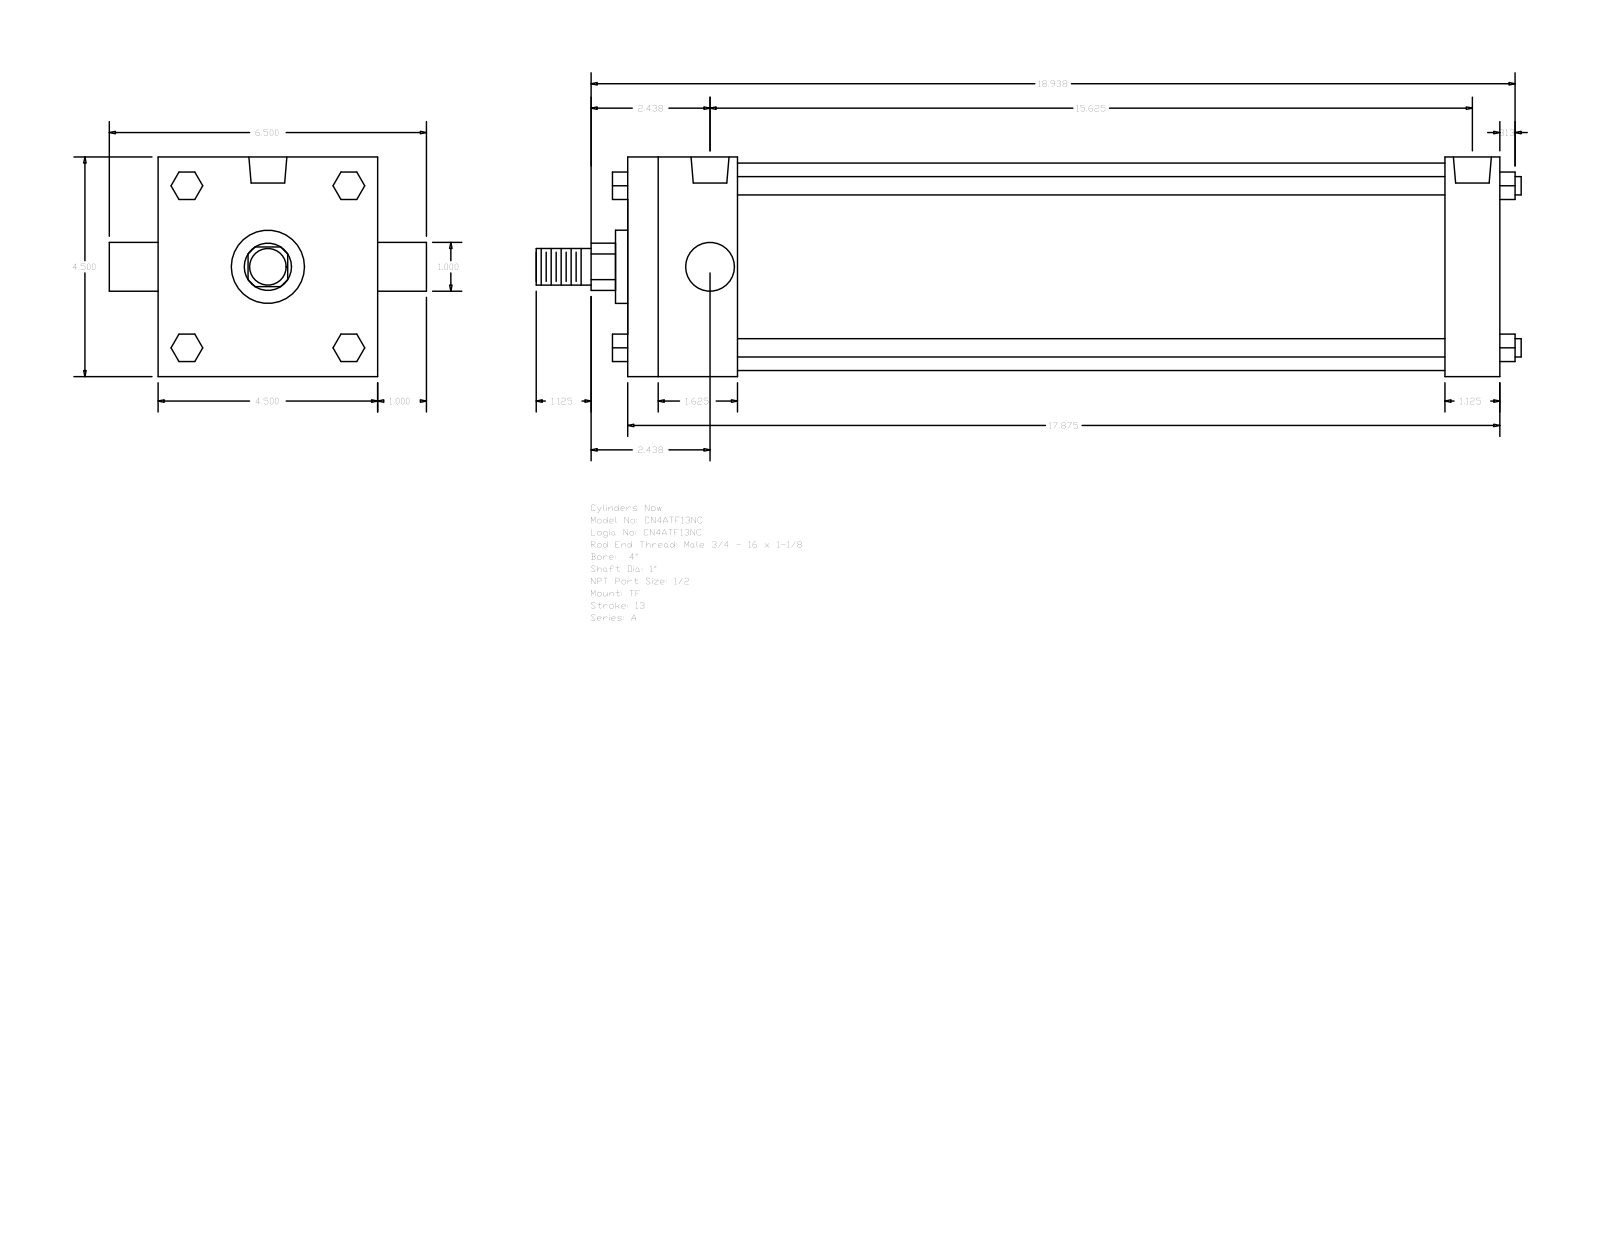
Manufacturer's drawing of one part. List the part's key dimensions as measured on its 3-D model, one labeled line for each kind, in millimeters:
Part name (STEP PRODUCT): A_TF__0400_1
STEP written by: GSSL Pune (CONFIG_CONTROL_DESIGN)
Units: millimetres
Bodies: 0 solids, 120 faces (92 planar, 28 cylindrical, 0 other)
Overall size (bounding box): 512.76 × 165.1 × 114.3
Round holes (diameter × count): ⌀8.73 ×3, ⌀19.77 ×2
Round bosses / shafts (diameter × count): ⌀9.53 ×4, ⌀25.4 ×2, ⌀107.95 ×1, ⌀38.1 ×1, ⌀19.05 ×1
Partial cylindrical surfaces — rounded edges, fillets, slot ends (radius × count): R12.29 ×1
Main face-to-face distances: 114.3, 454.02, 28.57, 425.45, 57.15, 368.3, 396.87, 14.29, 42.16, 73.03
Hole centre spacings: 3.18, 393.7, 390.52, 396.88
